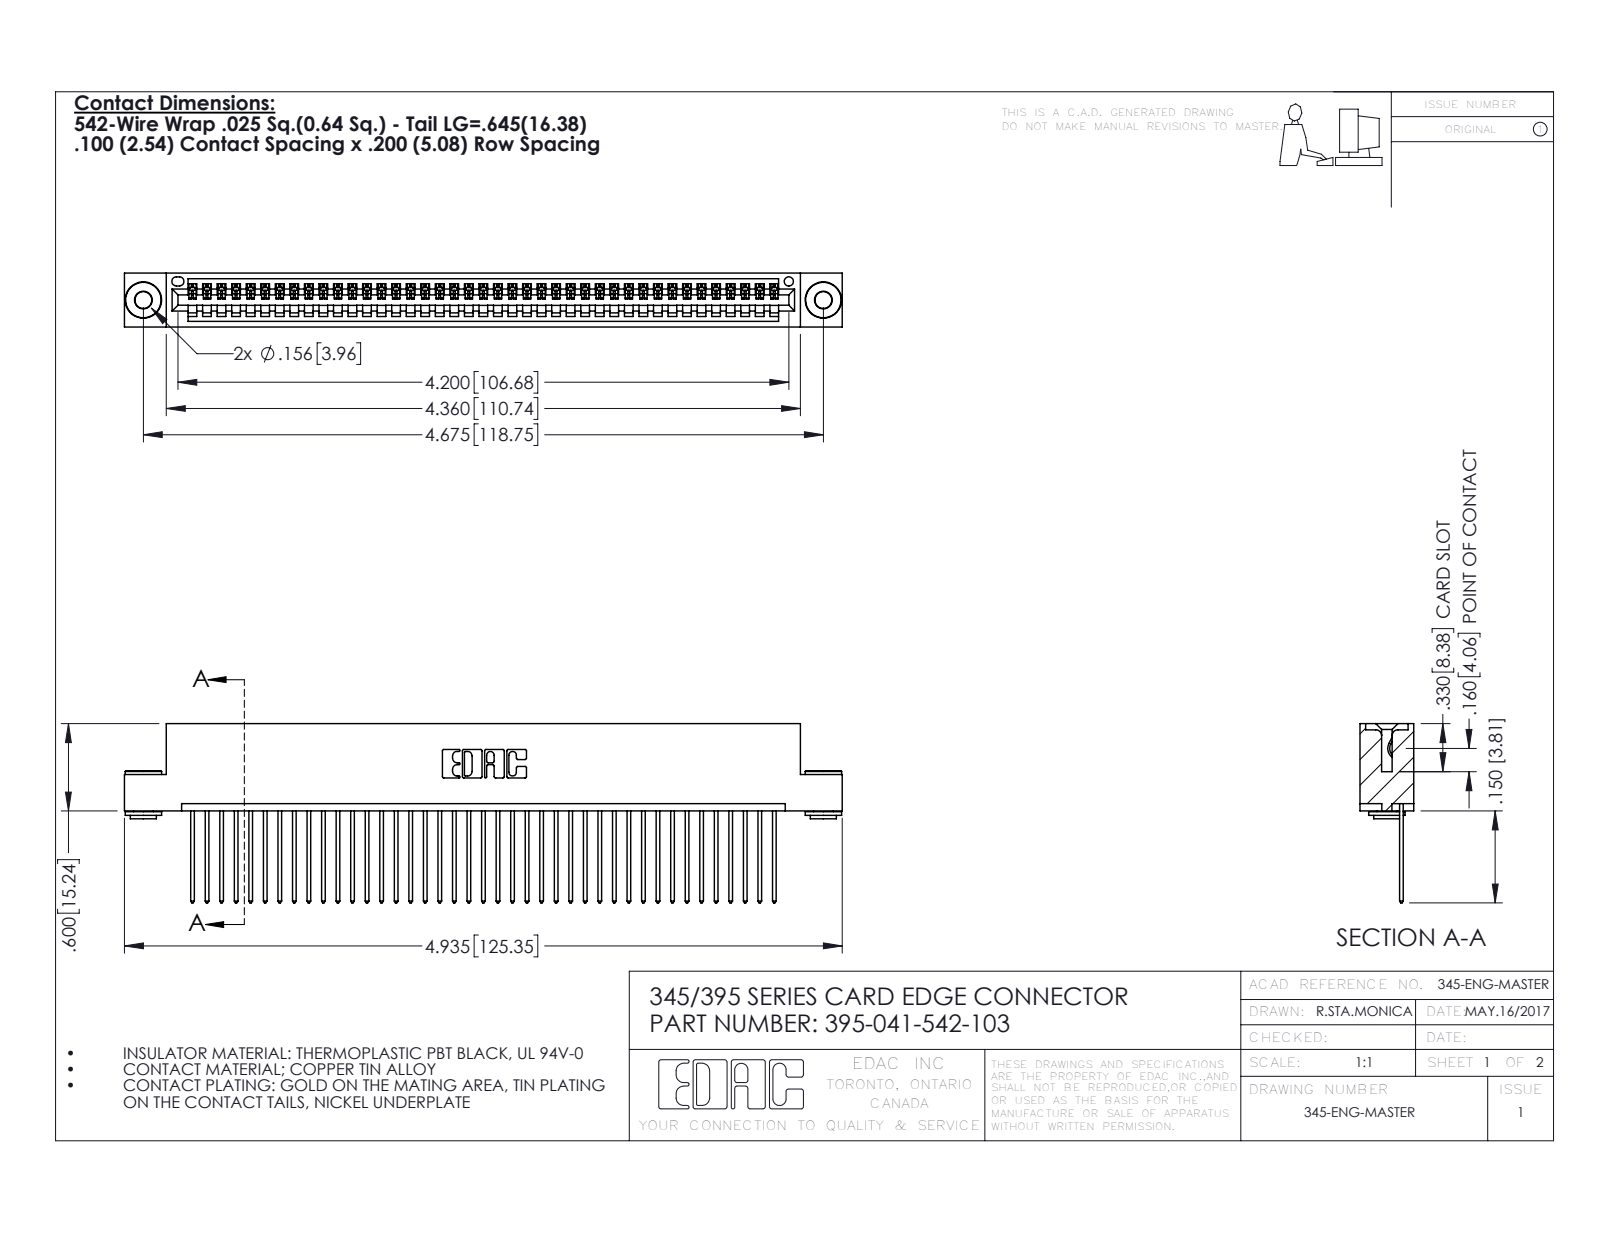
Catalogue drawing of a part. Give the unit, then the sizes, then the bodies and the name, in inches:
Units: inches
Overall size (bounding box): 4.935 × 1.232 × 0.37
Round holes (diameter × count): ⌀0.116 ×2, ⌀0.156 ×2, ⌀0.064 ×1
Round bosses / shafts (diameter × count): ⌀0.25 ×2, ⌀0.18 ×2, ⌀0.136 ×2
Partial cylindrical surfaces — rounded edges, fillets, slot ends (radius × count): R0.006 ×82, R0.01 ×82, R0.01 ×22, R0.007 ×6, R0.031 ×6, R0.026 ×3, R0.031 ×2, R0.04 ×2
Main face-to-face distances: 0.072, 0.298, 0.025, 0.37, 0.098, 0.272, 0.2, 0.225, 0.149, 0.072
Hole centre spacings: 0.27, 4.439, 4.675
Volume: 0.733 in³ · Surface area: 25.94 in²
Bodies: 44 solids, 2542 faces (1730 planar, 804 cylindrical, 8 other)
Part name (STEP PRODUCT): 345 Part_Flush Mounting Lugs - 0.156 Dia-TH; 345-250-002_345-250-002-102; 395-041-542-103; 345-292-001_345-293-142
STEP written by: SolidWorks 2016 (CONFIG_CONTROL_DESIGN)
